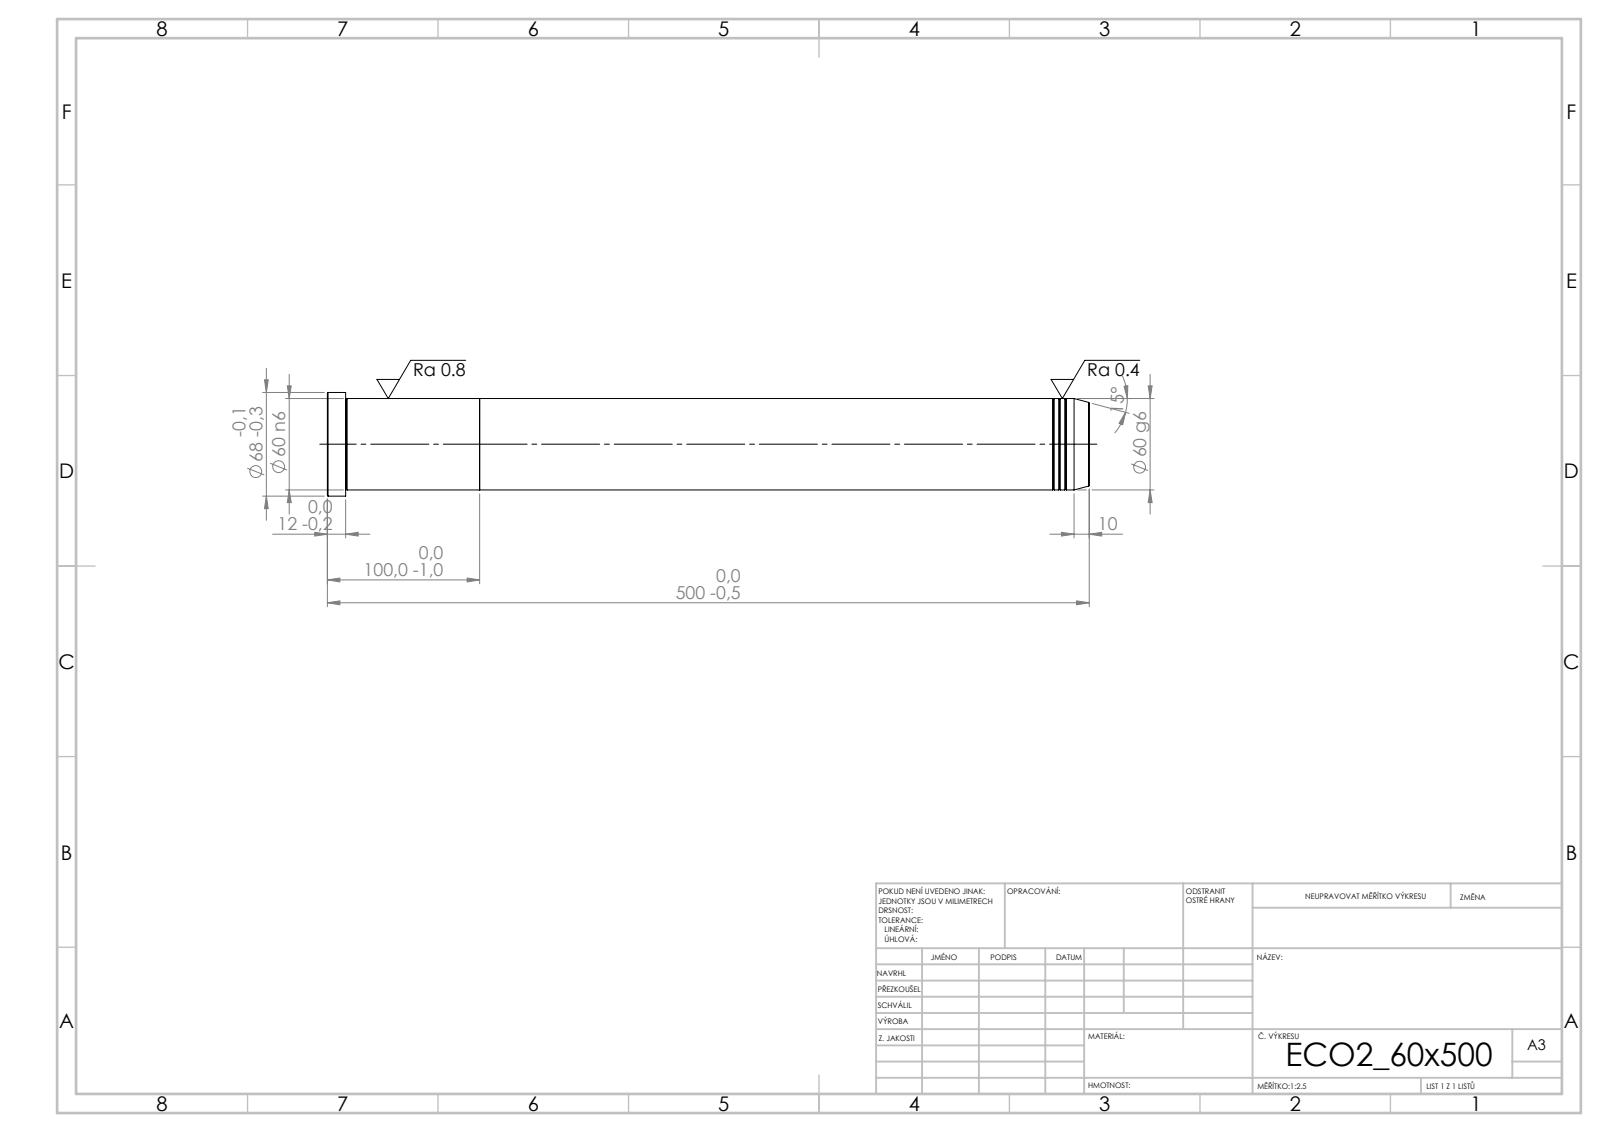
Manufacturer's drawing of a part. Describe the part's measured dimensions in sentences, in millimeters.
Its 3-D file was written by "SolidWorks 2019 (CONFIG_CONTROL_DESIGN)". It is 2 solids with 39 faces: 5 planar, 12 cylindrical and 22 other. Overall it measures 500 by 68 by 68 millimeters. Its volume is 1 421 000 cubic millimeters and its surface area 107 300 square millimeters. Round bosses or shafts: 1 of diameter 68, 1 of diameter 60. The main face-to-face distances are 100, 400, 500, 488, 88, 12.
